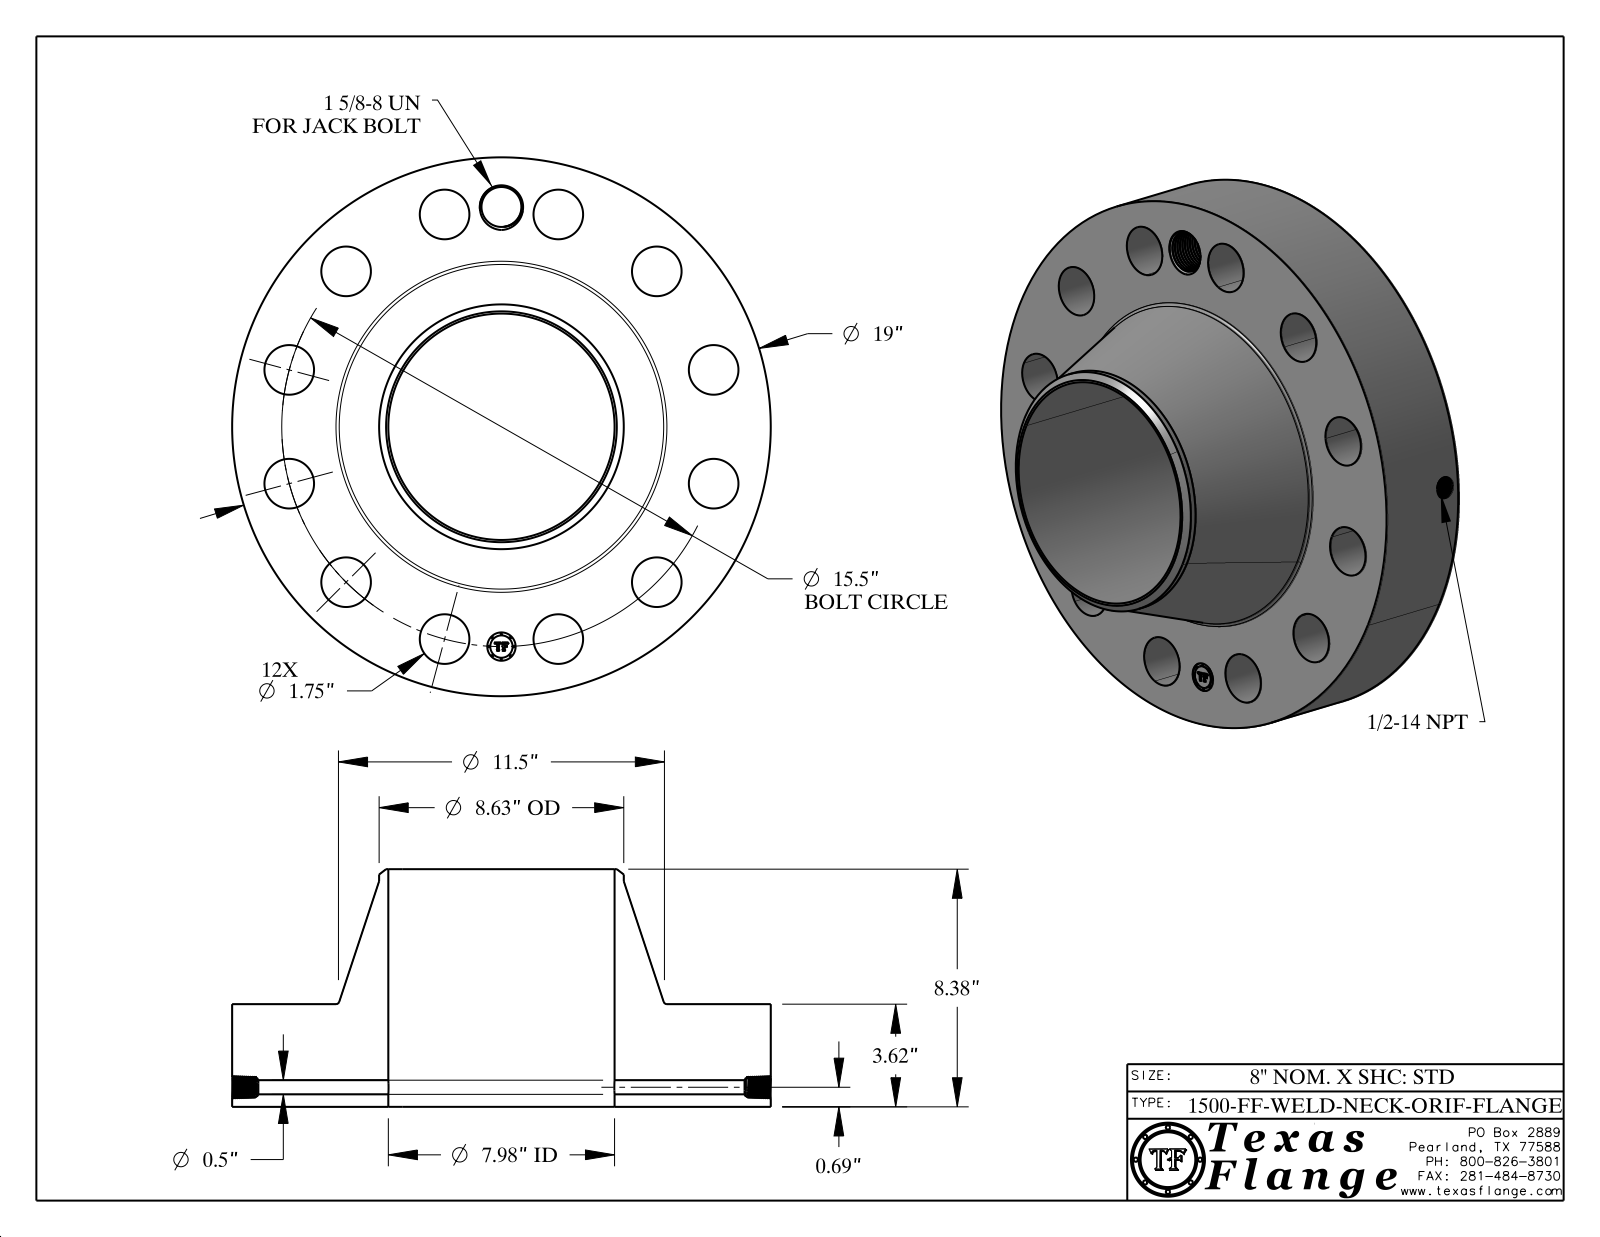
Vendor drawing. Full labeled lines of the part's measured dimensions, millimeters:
Part name (STEP PRODUCT): 1500-FF-WELD-NECK
STEP written by: CATIA V5 STEP AP214 (AUTOMOTIVE_DESIGN)
Units: millimetres
Bodies: 1 solid, 858 faces (368 planar, 127 cylindrical, 363 other)
Overall size (bounding box): 482.6 × 482.6 × 212.9
Volume: 14 180 000 mm³ · Surface area: 794 800 mm²
Round holes (diameter × count): ⌀44.5 ×12, ⌀12.7 ×1, ⌀17.1 ×1, ⌀25.4 ×1, ⌀35.8 ×1, ⌀202.7 ×1
Round bosses / shafts (diameter × count): ⌀1.5 ×8, ⌀482.6 ×1, ⌀219.2 ×1, ⌀20 ×1
Main face-to-face distances: 91.9, 212.9, 120.9, 91.6, 0.4, 121.3, 7.6, 7.4, 1.4, 6.3
Hole centre spacings: 196.9, 340.9, 380.3, 101.9, 196.9, 278.4, 393.7, 51.4
